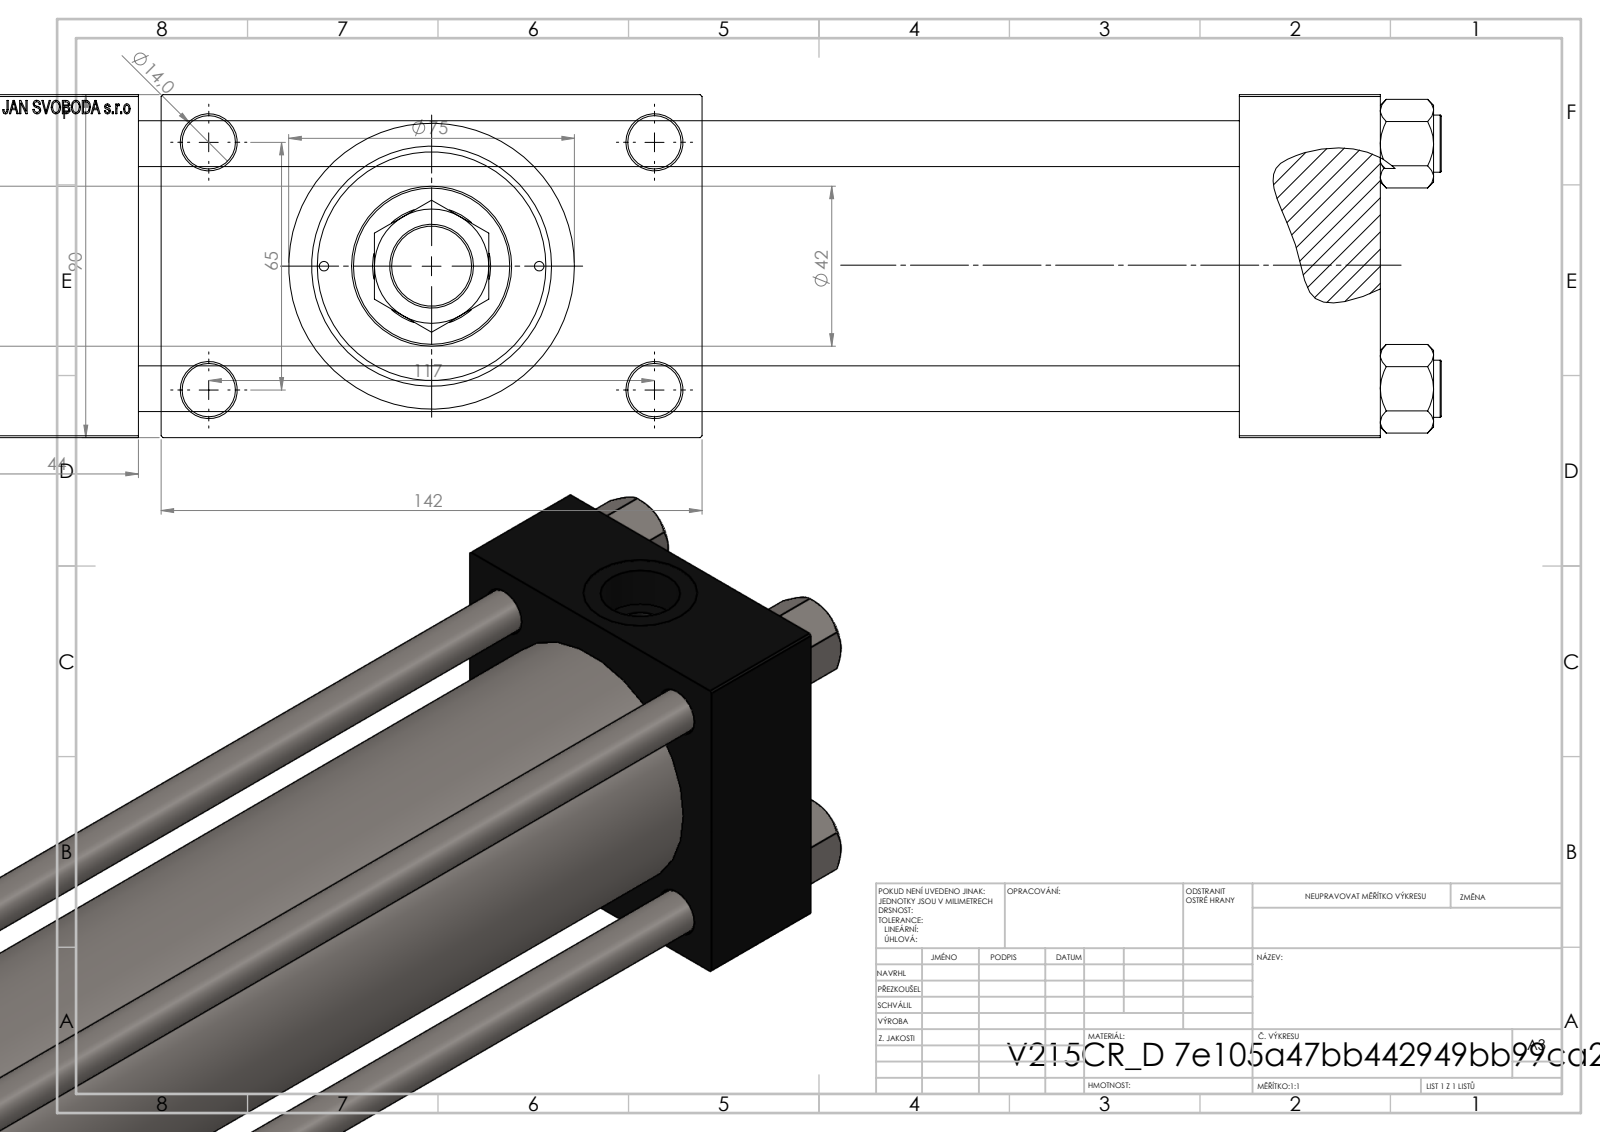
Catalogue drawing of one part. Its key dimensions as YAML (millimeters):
part_name: "V215CR_VCP_D; V215CR_D_Body; NUT_M5_D; V215CR_D_TYCINKA (+2 more)"
step_written_by: "SolidWorks 2019 (CONFIG_CONTROL_DESIGN)"
units: millimeters
bodies: {solids: 12, faces: 1164, planar: 515, cylindrical: 97, other: 552}
overall_size: [478, 142, 90]
volume: 1518000
surface_area: 354406
round_holes:
  - {diameter: 12, count: 4}
  - {diameter: 14, count: 4}
  - {diameter: 2.5, count: 2}
  - {diameter: 7, count: 2}
  - {diameter: 20.96, count: 2}
  - {diameter: 30, count: 2}
  - {diameter: 18.5, count: 1}
  - {diameter: 28, count: 1}
  - {diameter: 31, count: 1}
  - {diameter: 50, count: 1}
  - {diameter: 60, count: 1}
  - {diameter: 63, count: 1}
round_bosses_or_shafts:
  - {diameter: 15, count: 4}
  - {diameter: 75, count: 1}
  - {diameter: 69, count: 1}
  - {diameter: 42, count: 1}
  - {diameter: 22, count: 1}
  - {diameter: 14, count: 1}
partial_cylinders:
  - {radius: 13.5, count: 1}
face_to_face_distances: [90, 289, 37, 326, 333, 370, 44, 116, 26, 142]
hole_center_spacings: [26.35, 32.39, 44.4, 45.47, 64.3, 66.92, 68.42, 69.81]
